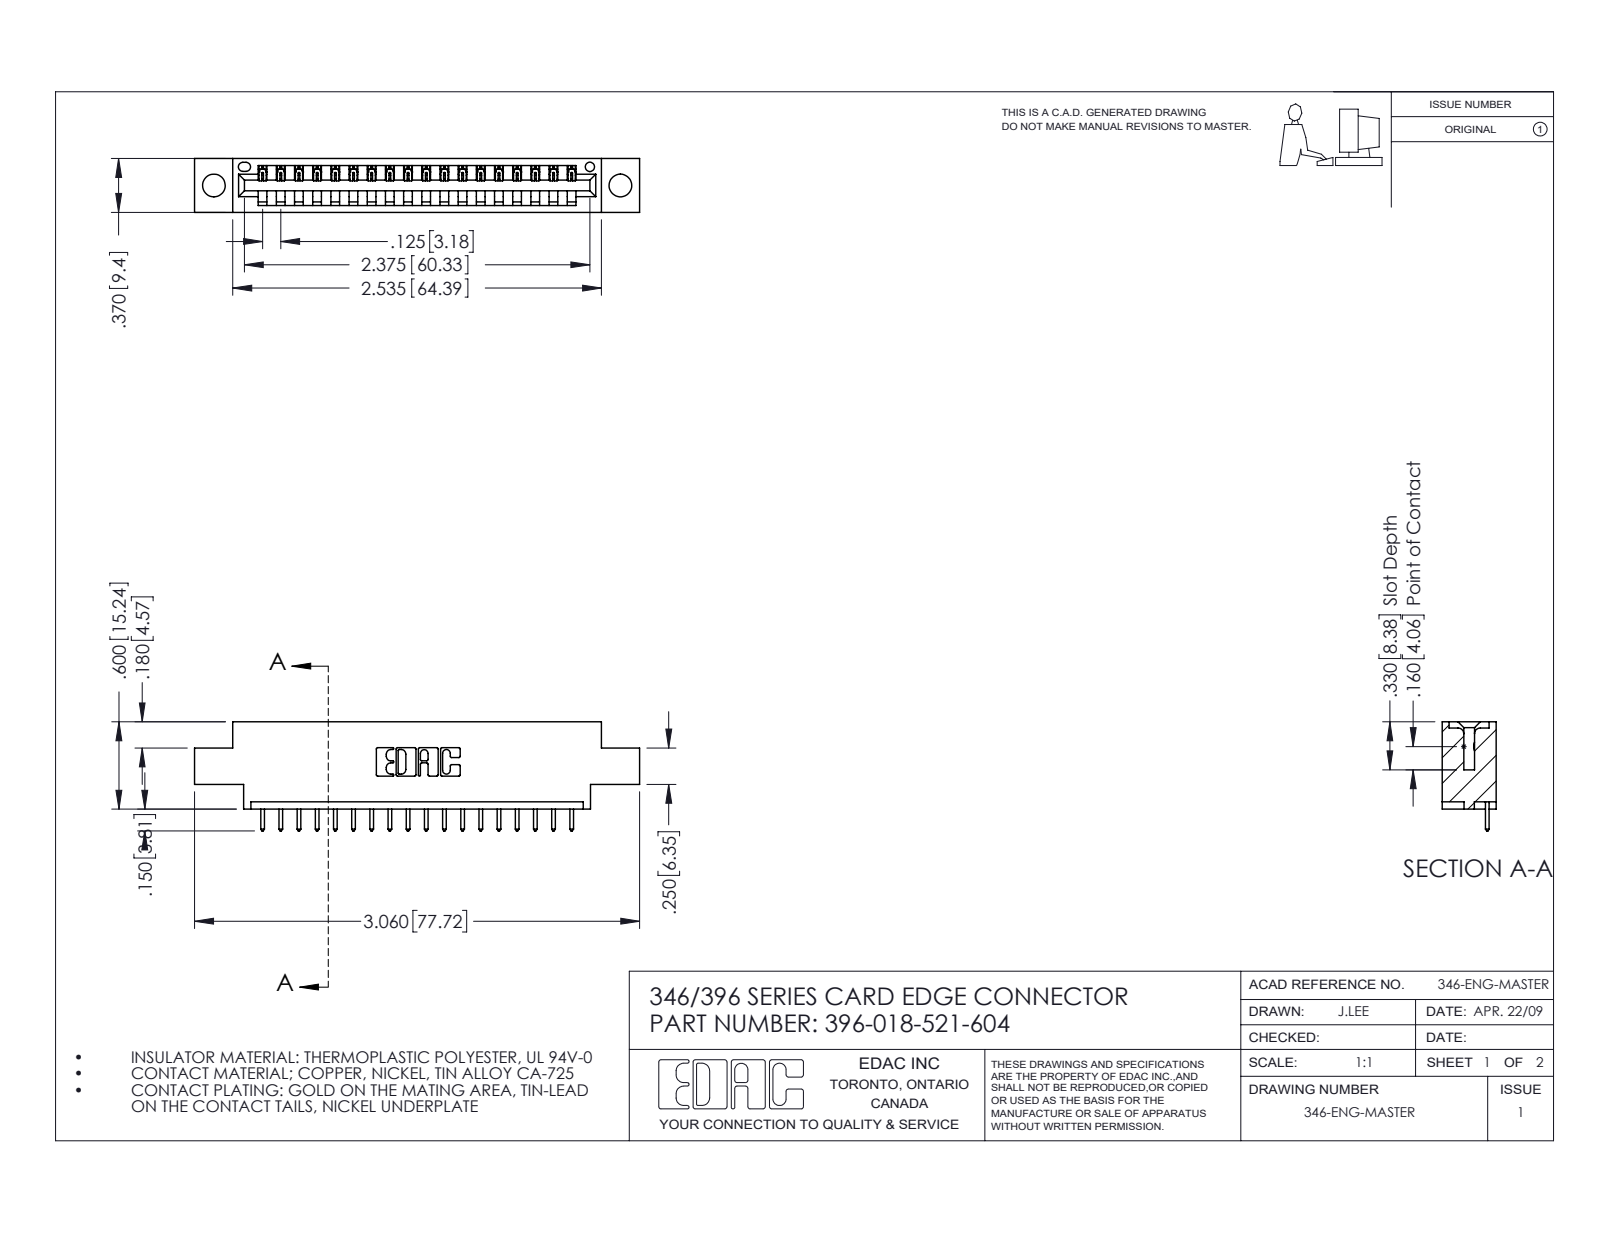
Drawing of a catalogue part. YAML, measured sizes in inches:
part_name: "346 Part_0.170 Offset - 0.156 Dia-TH; 345-292-001_345-293-121; 396-018-521-604"
step_written_by: "SolidWorks 2016 (CONFIG_CONTROL_DESIGN)"
units: inches
bodies: {solids: 19, faces: 1170, planar: 800, cylindrical: 370, other: 0}
overall_size: [3.06, 0.75, 0.37]
volume: 0.426
surface_area: 12.75
round_holes:
  - {diameter: 0.156, count: 2}
  - {diameter: 0.064, count: 1}
partial_cylinders:
  - {radius: 0.006, count: 36}
  - {radius: 0.01, count: 36}
  - {radius: 0.01, count: 22}
  - {radius: 0.007, count: 6}
  - {radius: 0.031, count: 6}
  - {radius: 0.026, count: 3}
  - {radius: 0.031, count: 2}
  - {radius: 0.04, count: 2}
face_to_face_distances: [0.048, 0.322, 0.37, 0.25, 0.072, 0.298, 0.025, 0.148, 0.222, 0.1]
hole_center_spacings: [0.246, 2.588, 2.795]
